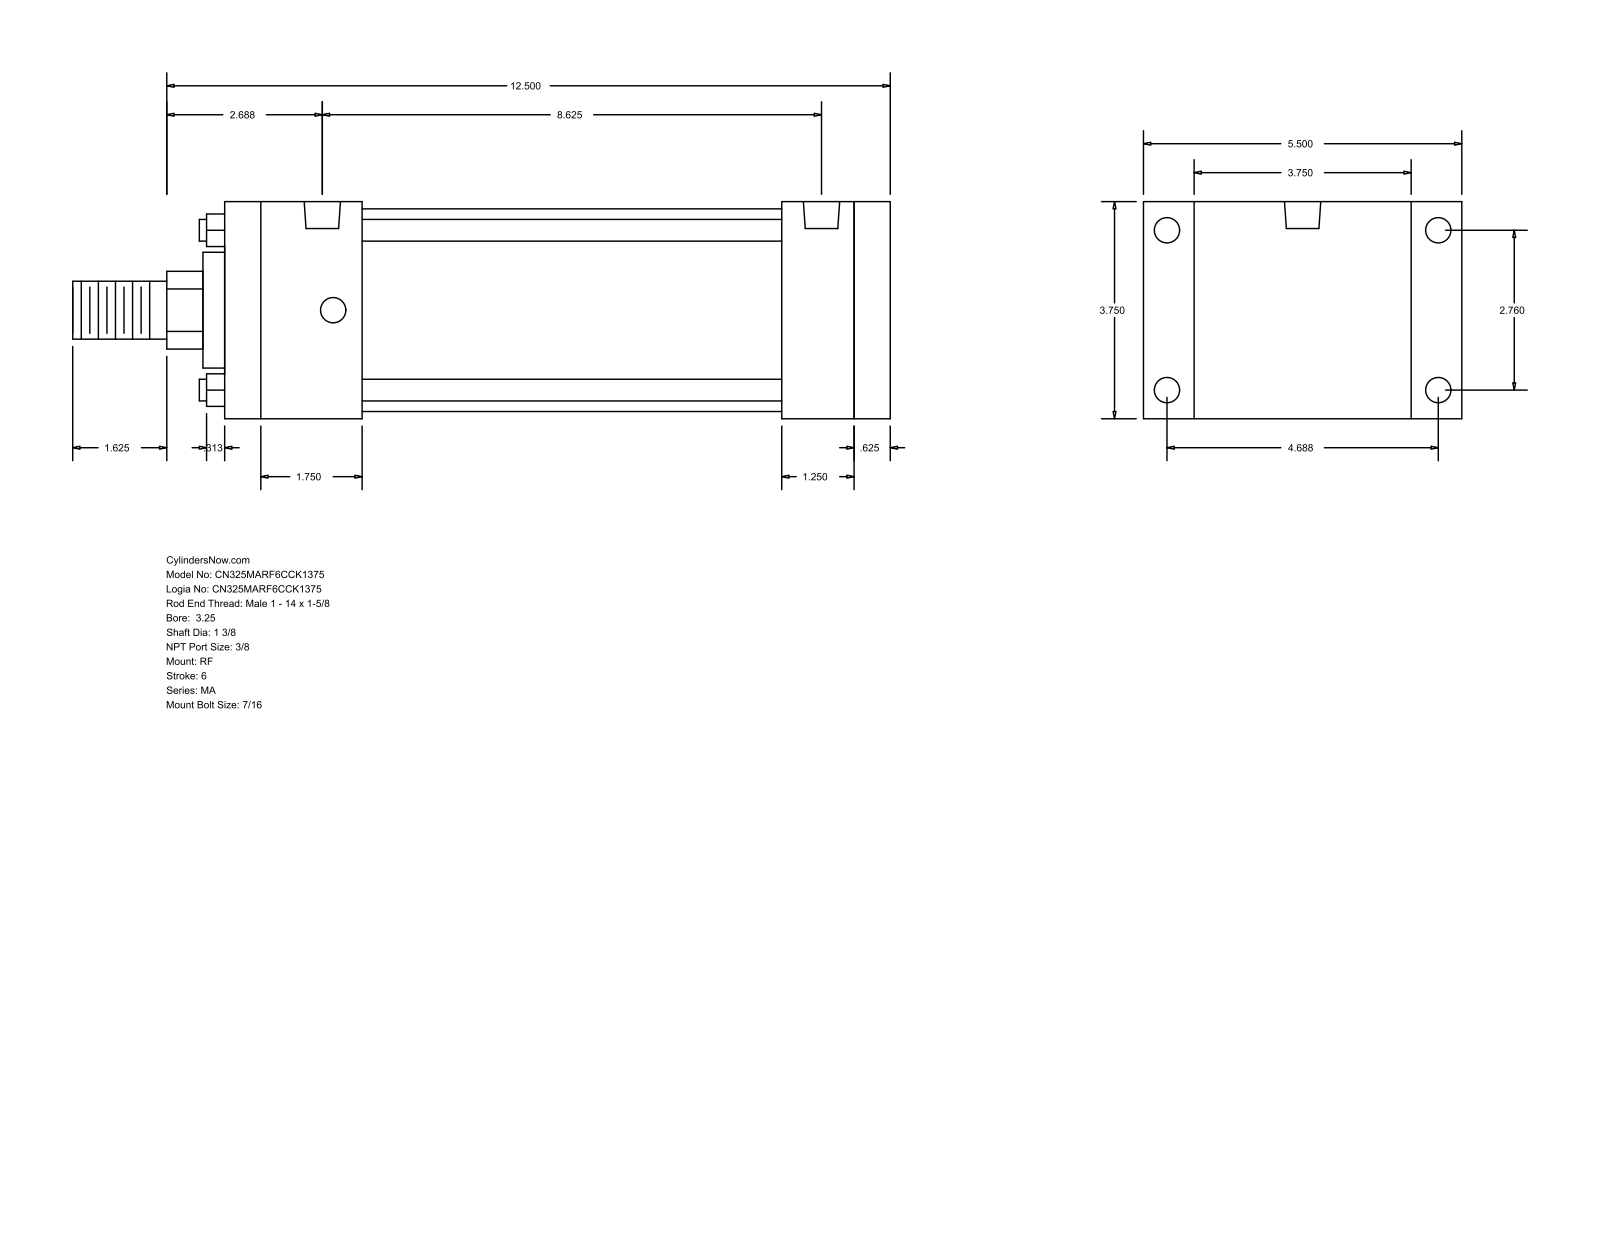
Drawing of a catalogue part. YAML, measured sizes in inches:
part_name: "MA_RF__0325_1.375"
step_written_by: "GSSL Pune (CONFIG_CONTROL_DESIGN)"
units: inches
bodies: {solids: 0, faces: 92, planar: 64, cylindrical: 28, other: 0}
overall_size: [14.125, 5.5, 3.75]
round_holes:
  - {diameter: 0.437, count: 8}
  - {diameter: 0.627, count: 2}
round_bosses_or_shafts:
  - {diameter: 0.375, count: 4}
  - {diameter: 3.5, count: 1}
  - {diameter: 2, count: 1}
  - {diameter: 1.375, count: 1}
  - {diameter: 1, count: 1}
partial_cylinders:
  - {radius: 0.672, count: 1}
face_to_face_distances: [3.75, 11.5, 0.625, 10.875, 0.875, 4.625, 9.625, 1.25, 1.875, 2.375]
hole_center_spacings: [0.188, 2.76, 4.687, 5.439, 8.25, 8.437, 8.625]
